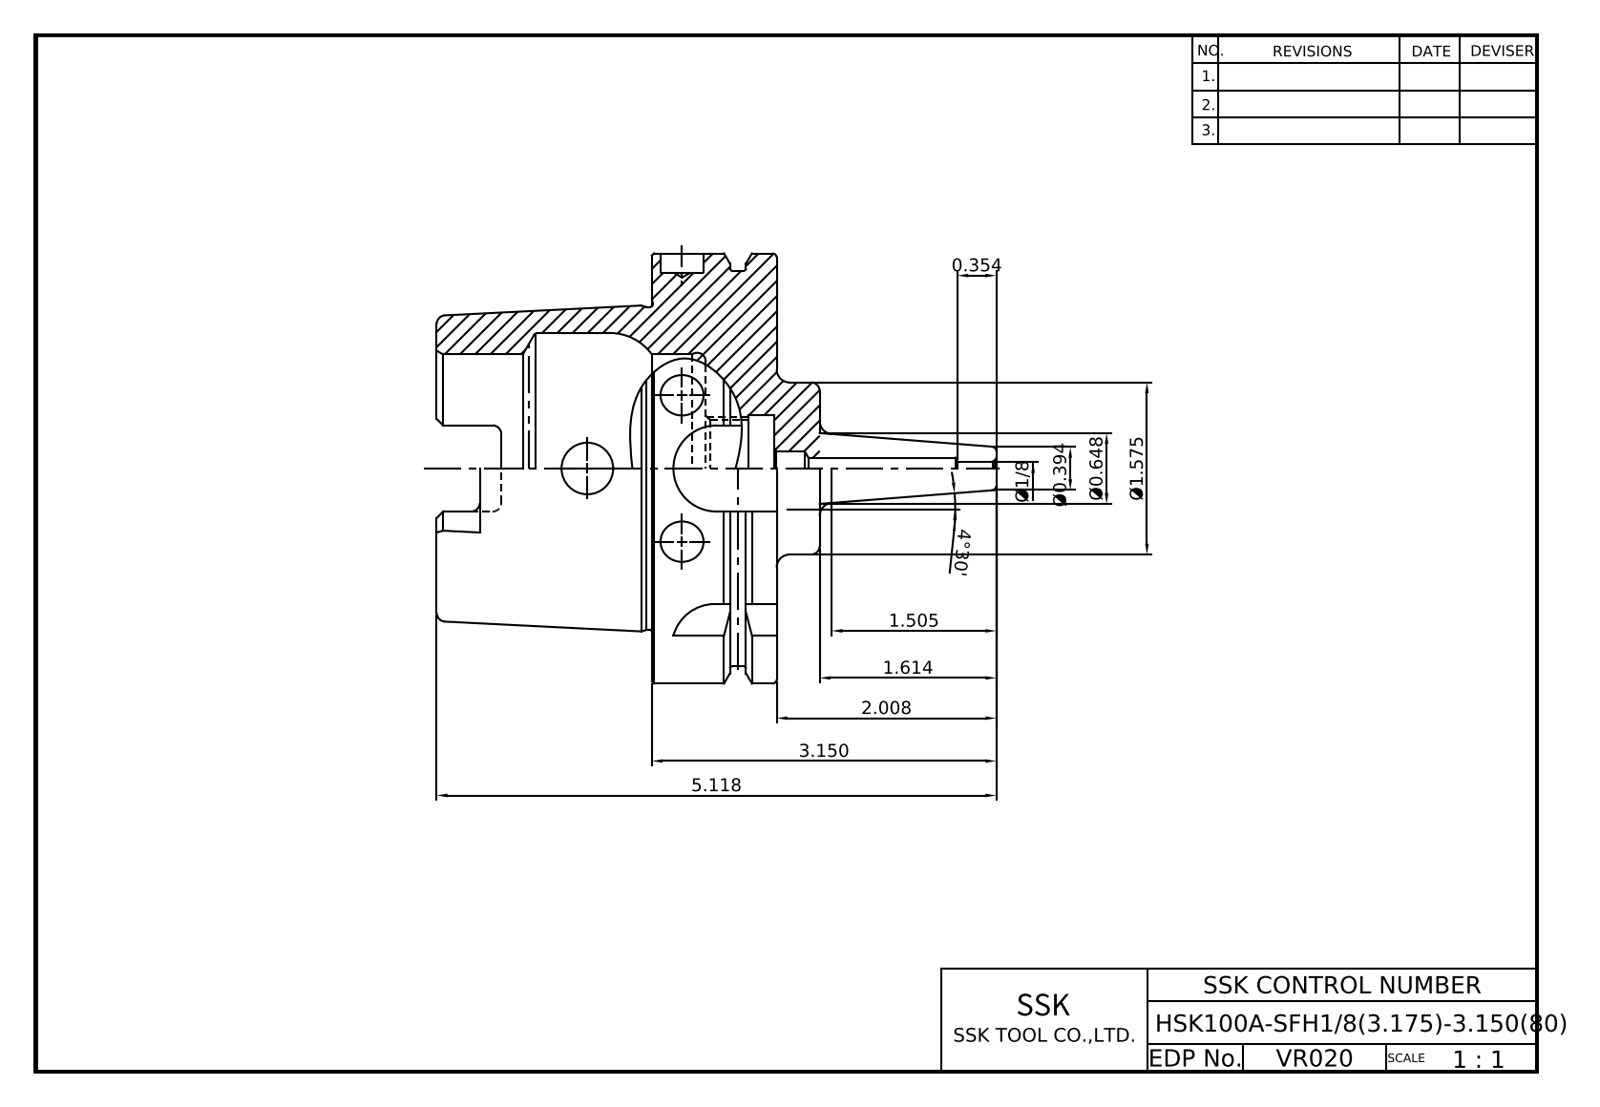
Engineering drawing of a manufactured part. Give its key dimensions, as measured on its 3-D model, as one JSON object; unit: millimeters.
{"part_name": "LO-HSK100A-SFH3.175-3.15", "step_written_by": "Autodesk Inventor 2022 (AUTOMOTIVE_DESIGN)", "units": "millimeters", "bodies": {"solids": 1, "faces": 120, "planar": 37, "cylindrical": 36, "other": 47}, "overall_size": [130, 100, 100], "volume_mm3": 271118, "surface_area_mm2": 53130, "round_holes": [[10, 3], [3.17, 1], [5, 1], [8, 1], [12, 1], [22.38, 1], [25, 1], [53, 1], [63, 1]], "round_bosses_or_shafts": [[100, 1], [92, 1], [75.41, 1], [40, 1]], "partial_cylinders_radius": [[2, 6], [4.88, 4], [10, 4]], "face_to_face_distances": [29, 12.5, 16.5, 79, 62.5, 10, 50, 89, 39, 26.5]}
